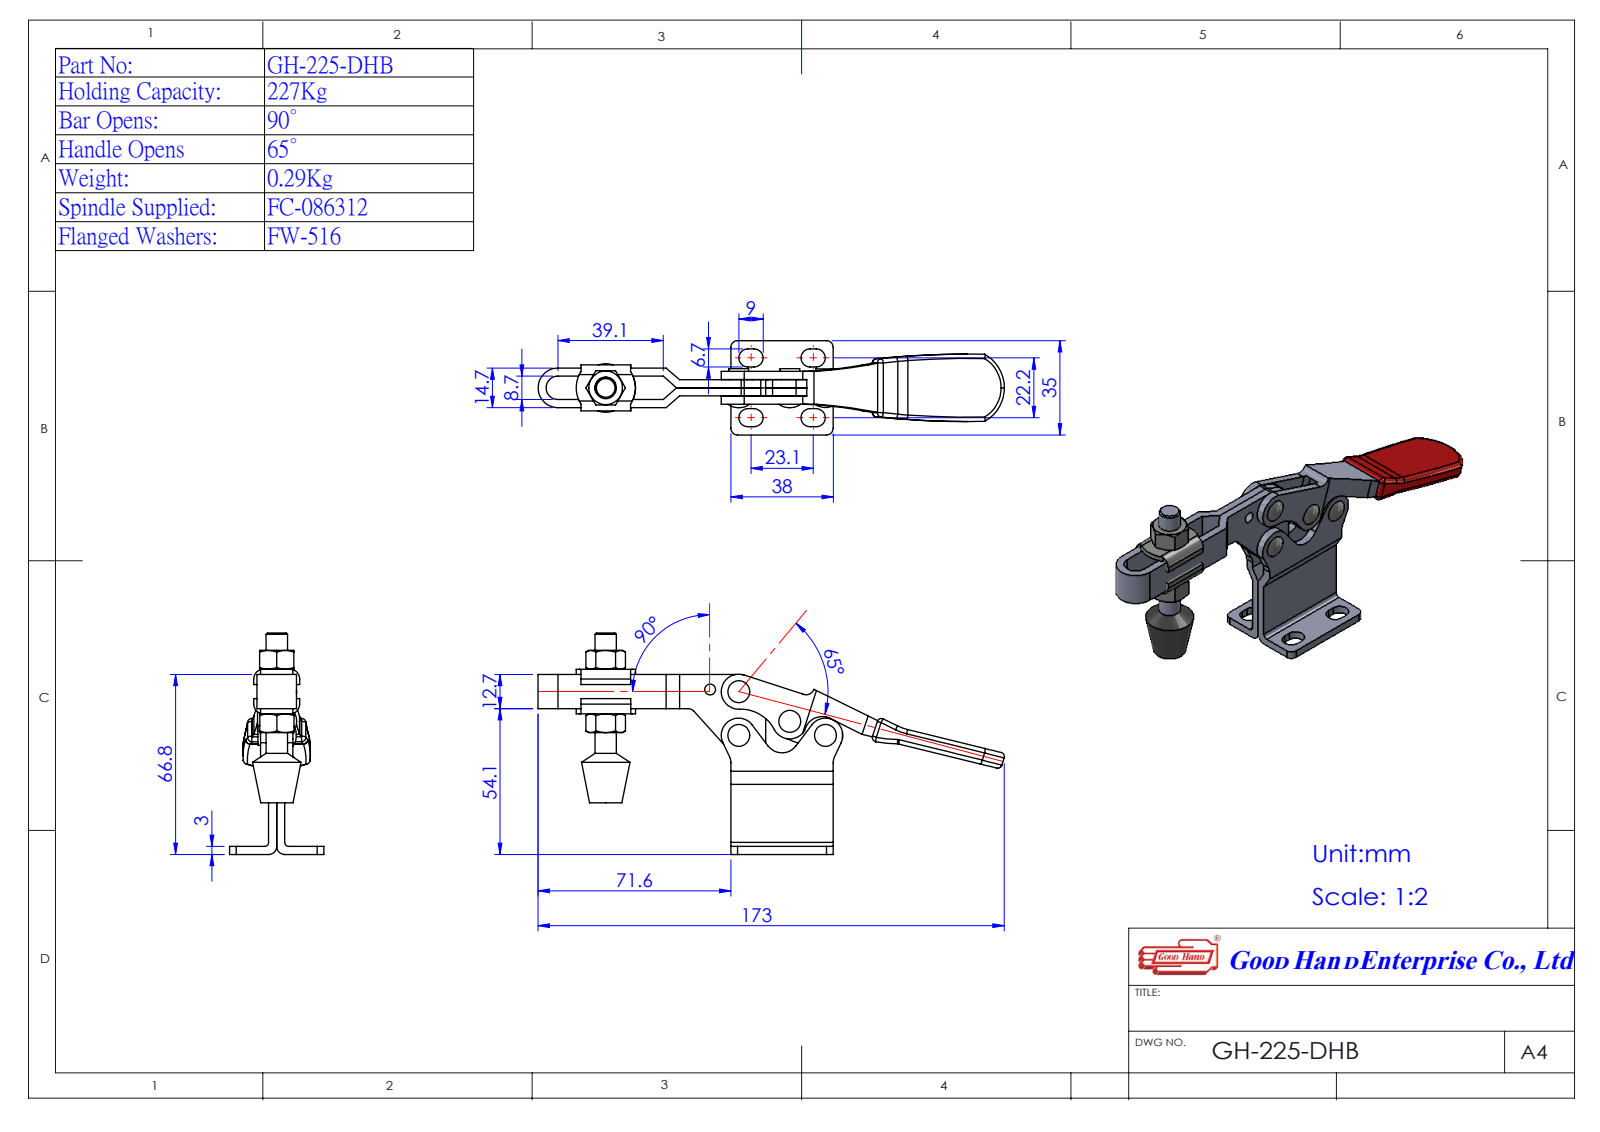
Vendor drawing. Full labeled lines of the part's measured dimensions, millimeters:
Part name (STEP PRODUCT): 1225D08-1^GH-225-DHB(簡化)-1; Group1^GH-225-DHB(簡化); GH-225-DHB(簡化)-1; Group1^GH-225-DHB(簡化)-1 (+2 more)
STEP written by: SolidWorks 2016 (AUTOMOTIVE_DESIGN)
Units: millimetres
Bodies: 4 solids, 297 faces (132 planar, 138 cylindrical, 27 other)
Overall size (bounding box): 173.56 × 82.2 × 35
Volume: 31 935 mm³ · Surface area: 28 819 mm²
Round holes (diameter × count): ⌀5 ×4
Round bosses / shafts (diameter × count): ⌀7.35 ×4, ⌀6.35 ×2, ⌀6.3 ×2, ⌀7.93 ×1, ⌀5 ×1, ⌀4 ×1
Partial cylindrical surfaces — rounded edges, fillets, slot ends (radius × count): R3.35 ×8, R3 ×7, R1.2 ×4, R2.5 ×4, R3.6 ×4, R11.04 ×4, R6.4 ×3, R6.5 ×3
Main face-to-face distances: 3, 6, 3.1, 6.1, 9.1, 3.01, 2.99, 9, 7.35, 10.36
Hole centre spacings: 14.25, 16.2, 19.73, 21.99, 32.3, 36.13
